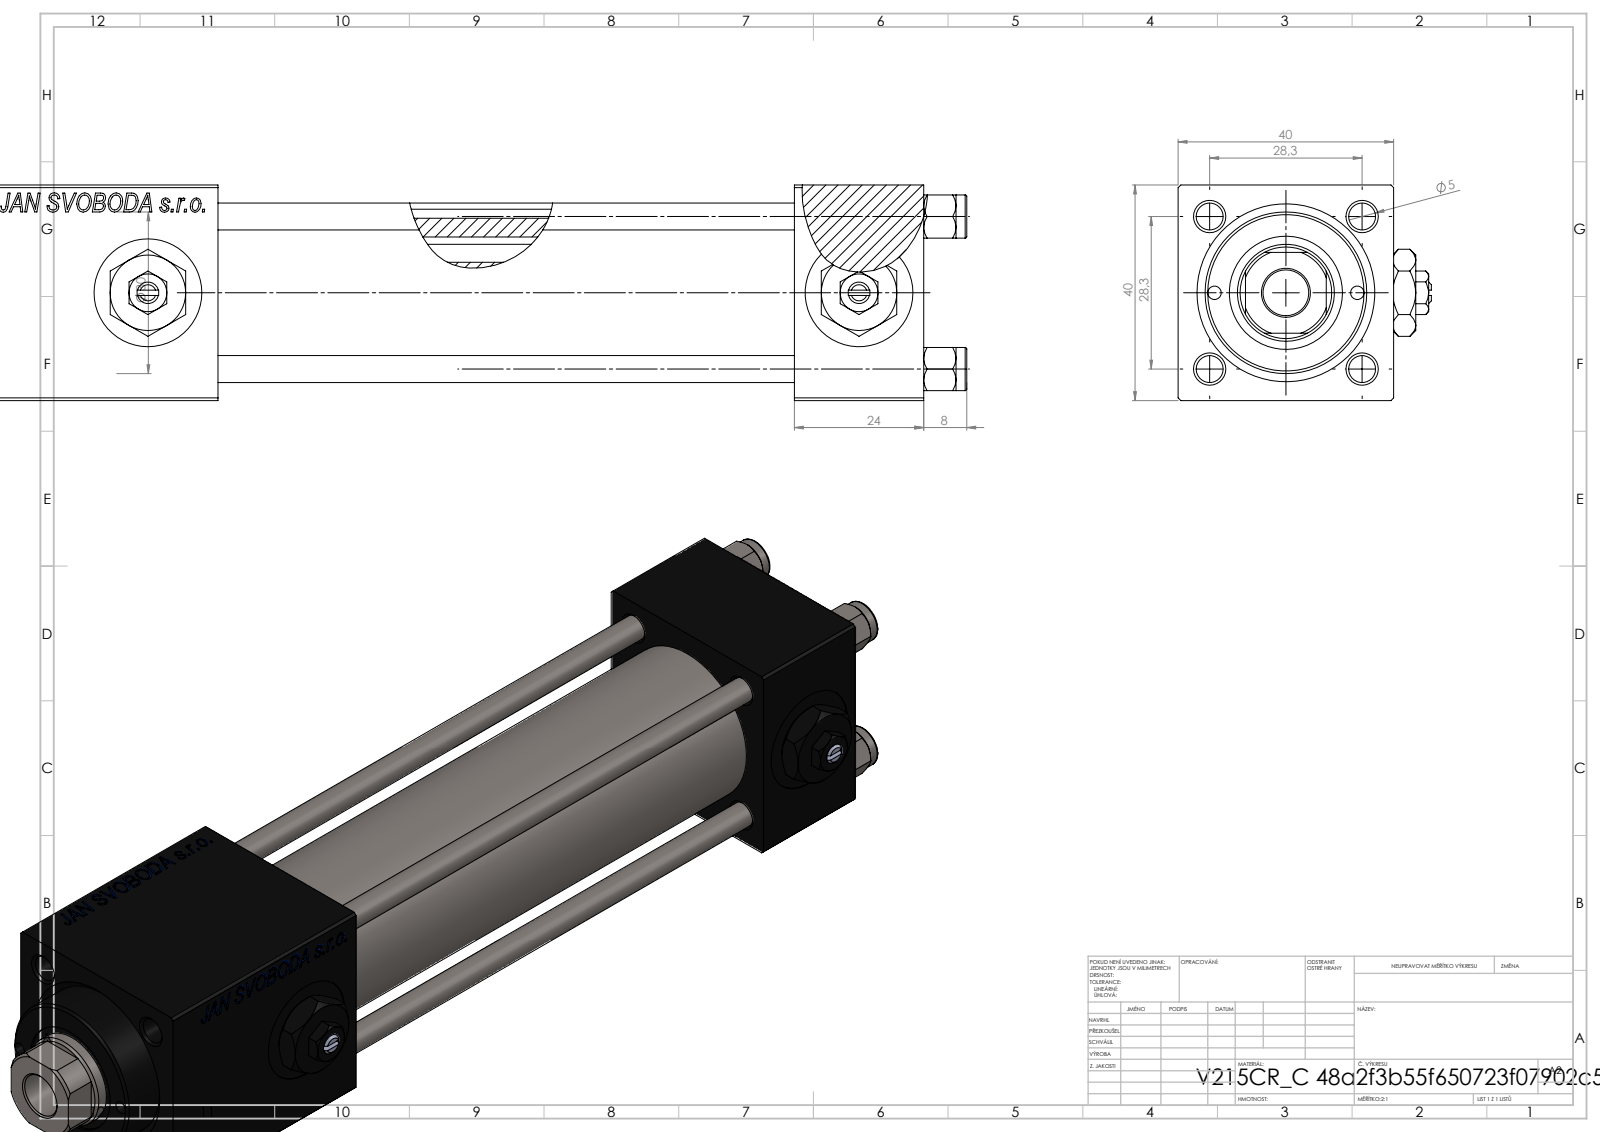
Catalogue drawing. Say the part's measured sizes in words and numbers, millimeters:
The part is named "V215CR_C_Body; V215_VC_A; V215CR_VCP_C; NUT_M5_C (+2 more)". Its 3-D file was written by "SolidWorks 2019 (CONFIG_CONTROL_DESIGN)". It is 13 solids with 1251 faces: 573 planar, 100 cylindrical and 578 other. Overall it measures 202 by 47 by 40 millimeters. Its volume is 184 289 cubic millimeters and its surface area 76 392 square millimeters. Round holes: 4 of diameter 5, 3 of diameter 20, 2 of diameter 2.5, 2 of diameter 7, 2 of diameter 13.16, 1 of diameter 8.5, 1 of diameter 18, 1 of diameter 21, 1 of diameter 25, 1 of diameter 30. Round bosses or shafts: 4 of diameter 8, 1 of diameter 31. Partial cylindrical surfaces (rounded edges, fillets, slot ends): 1 of radius 8.5. The main face-to-face distances are 40, 24, 39.8, 131, 107, 150.3, 126.3, 19.3, 48, 155. The hole center spacings are 14.18, 20.01, 28.3, 30.84, 13.25, 40.02, 26.5, 132.
